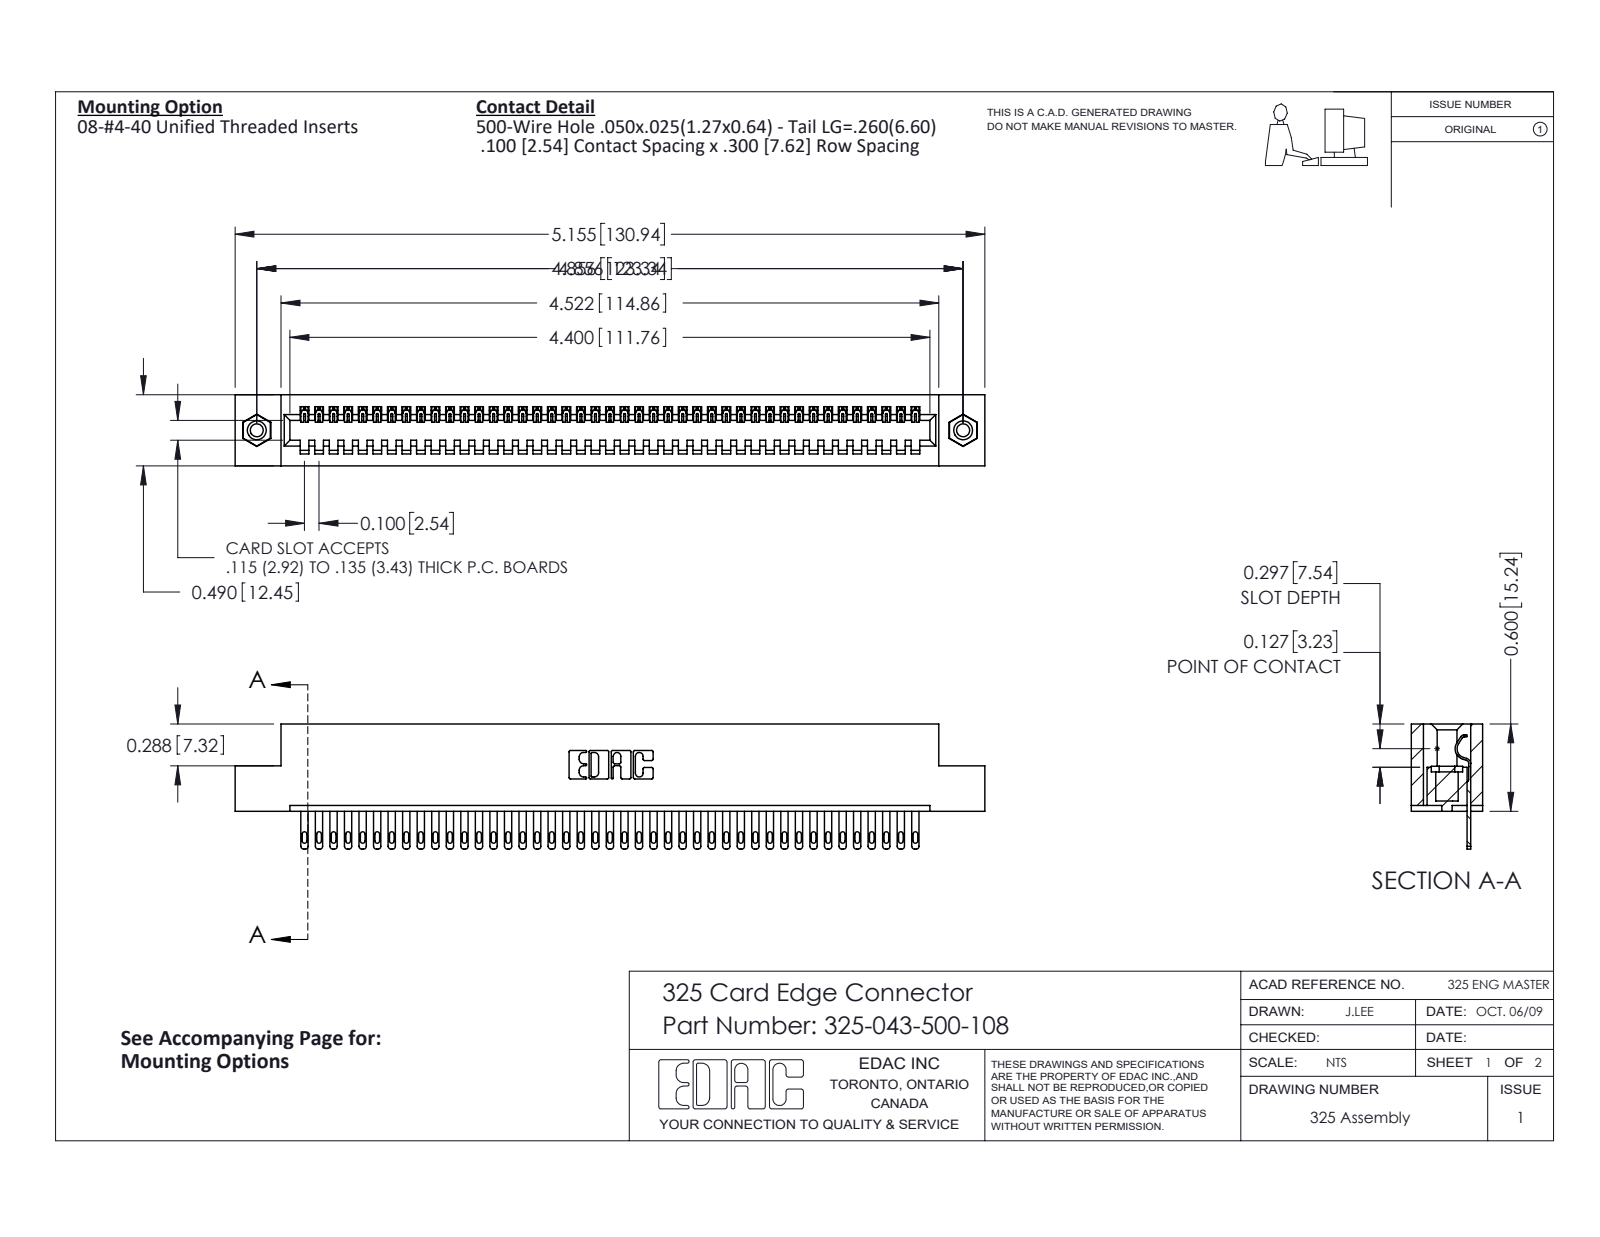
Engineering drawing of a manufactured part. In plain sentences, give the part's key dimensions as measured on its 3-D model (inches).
The part is named "325-292-001_325-293-100; 325 Part_TI; 345-250-001_345-250-003-102; 325-043-500-108". Its 3-D file was written by "SolidWorks 2016 (CONFIG_CONTROL_DESIGN)". It is 46 solids with 2496 faces: 1650 planar, 830 cylindrical and 16 other. Overall it measures 5.155 by 0.86 by 0.49 inches. Its volume is 1.016 cubic inches and its surface area 28.4 square inches. Round holes: 2 of diameter 0.089, 2 of diameter 0.125, 2 of diameter 0.16. Round bosses or shafts: 2 of diameter 0.155. Partial cylindrical surfaces (rounded edges, fillets, slot ends): 86 of radius 0.006, 86 of radius 0.016, 86 of radius 0.02, 22 of radius 0.01, 6 of radius 0.007, 6 of radius 0.031, 3 of radius 0.026, 1 of radius 0.014. The main face-to-face distances are 0.083, 0.407, 0.49, 0.3, 0.107, 0.383, 0.025, 0.325, 0.56, 0.04. The hole center spacings are 4.856.
